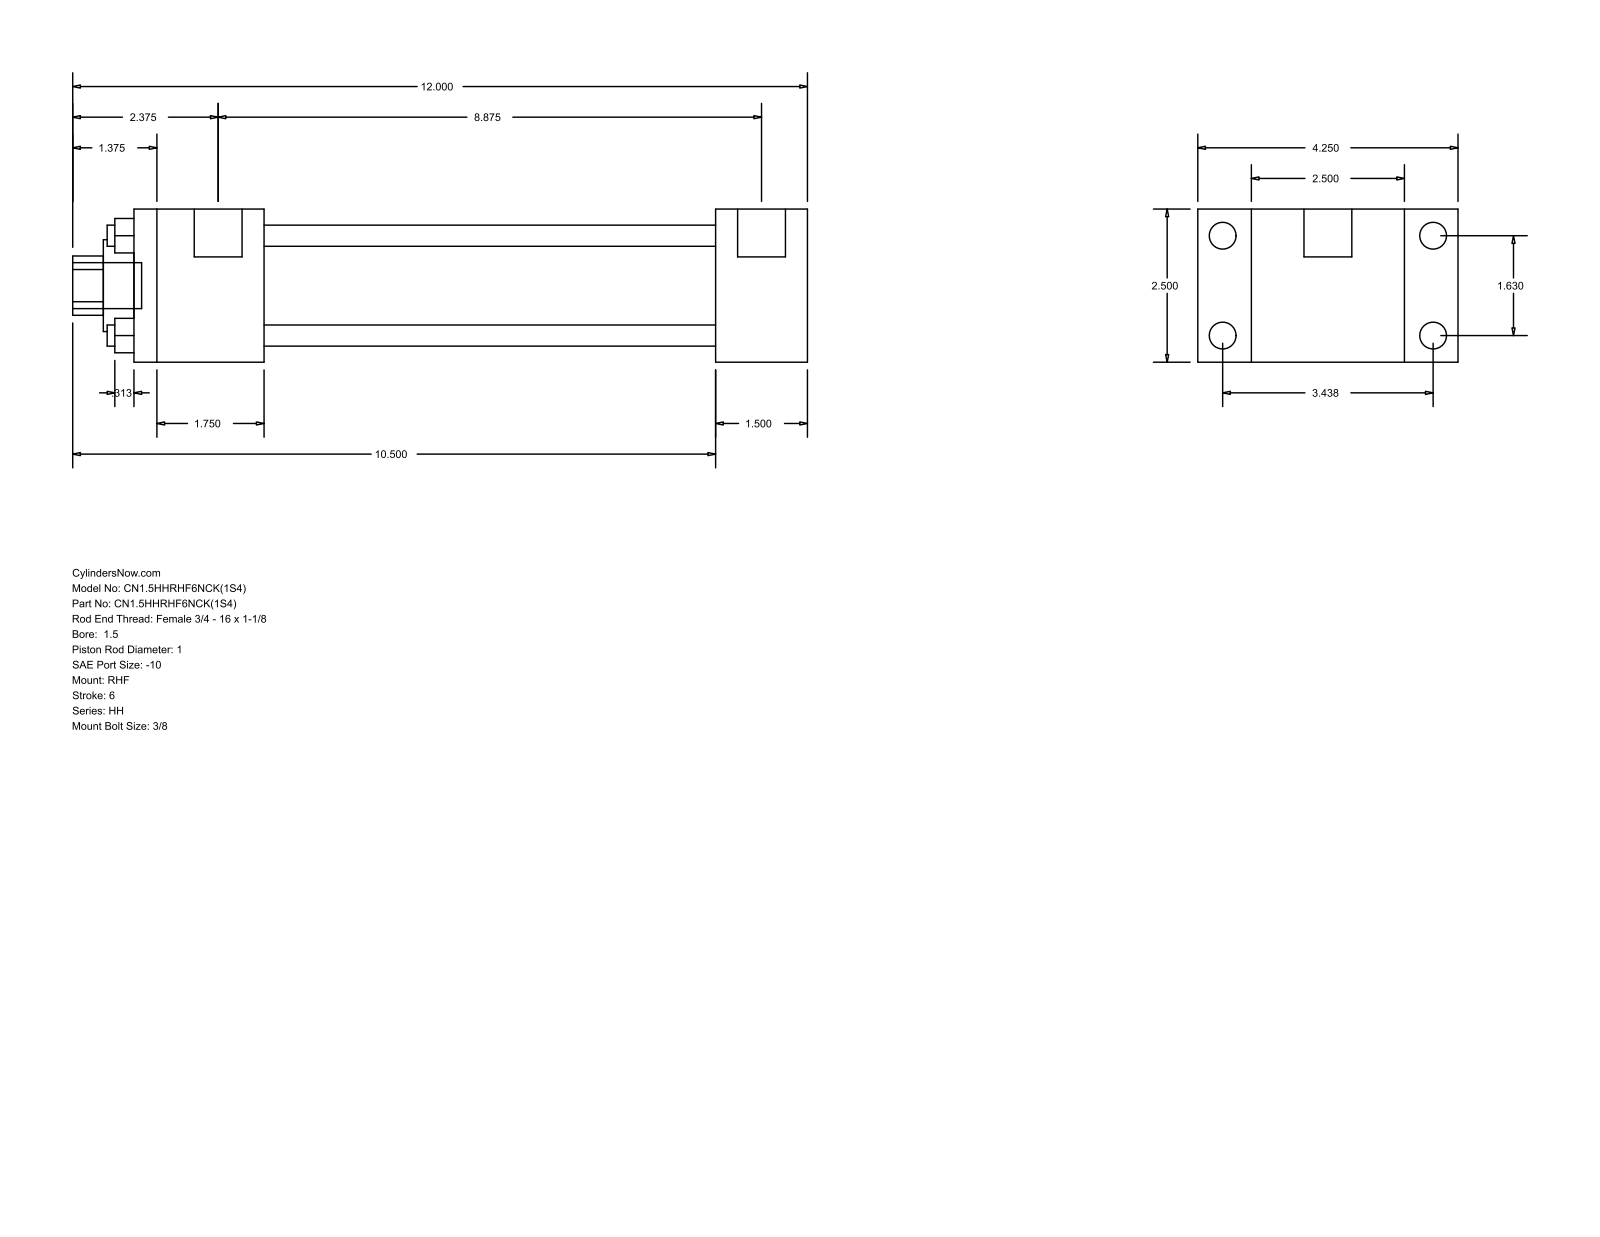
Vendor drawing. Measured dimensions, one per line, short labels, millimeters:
name: HH_RHF__0150_1
written by: GSSL Pune (CONFIG_CONTROL_DESIGN)
unit: mm
bodies: 0 solids, 88 faces (60 planar, 28 cylindrical, 0 other)
size: 304.8 × 107.95 × 63.5
holes: 4× ⌀8.76, 1× ⌀25.4, 1× ⌀38.1, 1× ⌀44.45
bosses: 4× ⌀11.13, 4× ⌀5.56, 2× ⌀19.84, 1× ⌀19.05
rounds: 1× R12.29
face distances: 63.5, 22.23, 85.73, 38.1, 107.96, 187.32, 225.42, 53.98, 241.3, 279.4
hole spacings: 29.27, 41.4, 58.55
